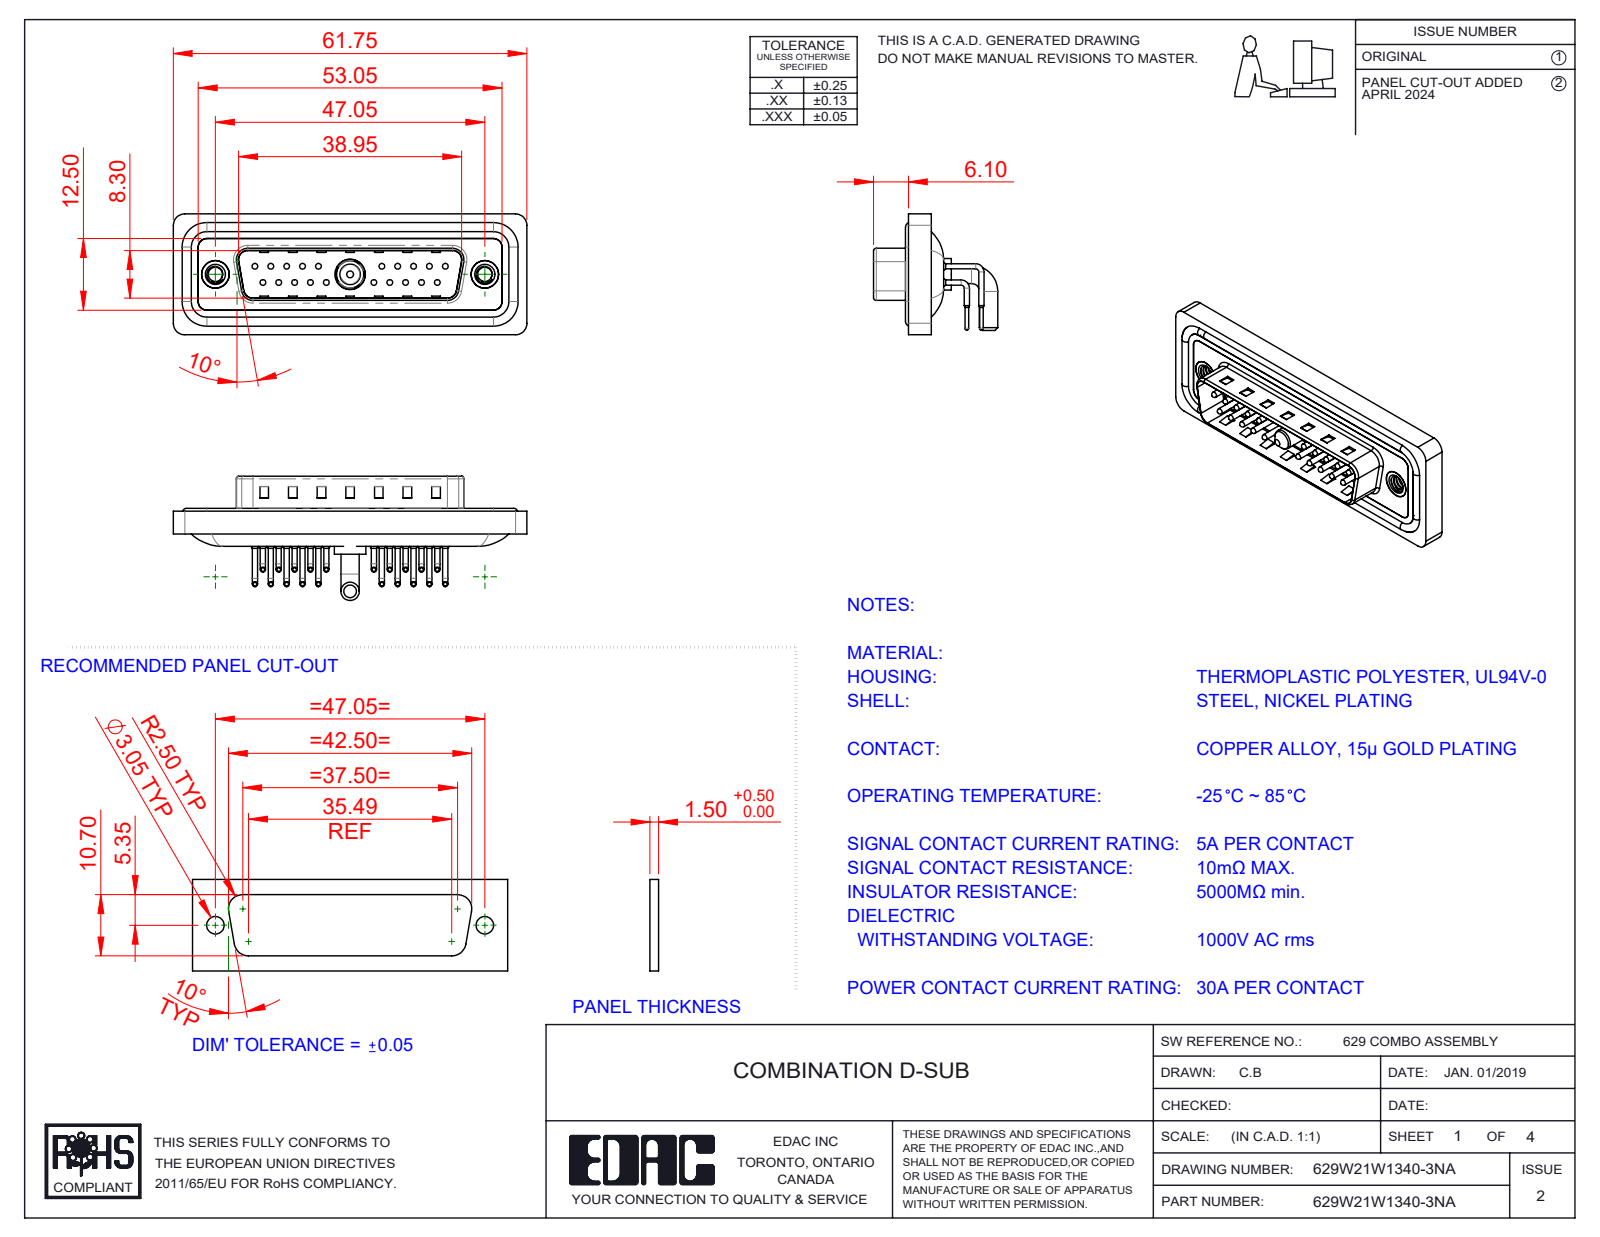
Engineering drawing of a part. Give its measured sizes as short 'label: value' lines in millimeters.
name: 629Combo Housing_21W1; 629Combo Contact Row 1; 629Combo Contact Row 2; 629Combo Shell Rear_25 Contacts (+5 more)
written by: SolidWorks 2023 (CONFIG_CONTROL_DESIGN)
unit: mm
bodies: 29 solids, 2720 faces (1499 planar, 927 cylindrical, 294 other)
size: 61.75 × 21.7 × 21.1
volume: 7 450 mm³; area: 12 743 mm²
holes: 20× ⌀0.75, 20× ⌀1.6, 20× ⌀2, 2× ⌀2.5, 2× ⌀4, 2× ⌀4.8, 2× ⌀5, 1× ⌀4.85, 1× ⌀5.3
bosses: 40× ⌀0.9, 20× ⌀1.5, 20× ⌀1, 20× ⌀0.65, 4× ⌀1.6, 2× ⌀4.9, 2× ⌀3.2, 1× ⌀5.5
rounds: 20× R1.01, 18× R1.5, 18× R2, 8× R0.5, 8× R1.6, 4× R0.25, 4× R0.6, 4× R0.65
face distances: 0.4, 2.9, 0.8, 4.1, 1.1, 2.1, 1.6, 4.5, 1.5, 2.5
hole spacings: 3.16, 2.77, 5.54, 8.31, 5.04, 19.39, 20.97, 22.16
